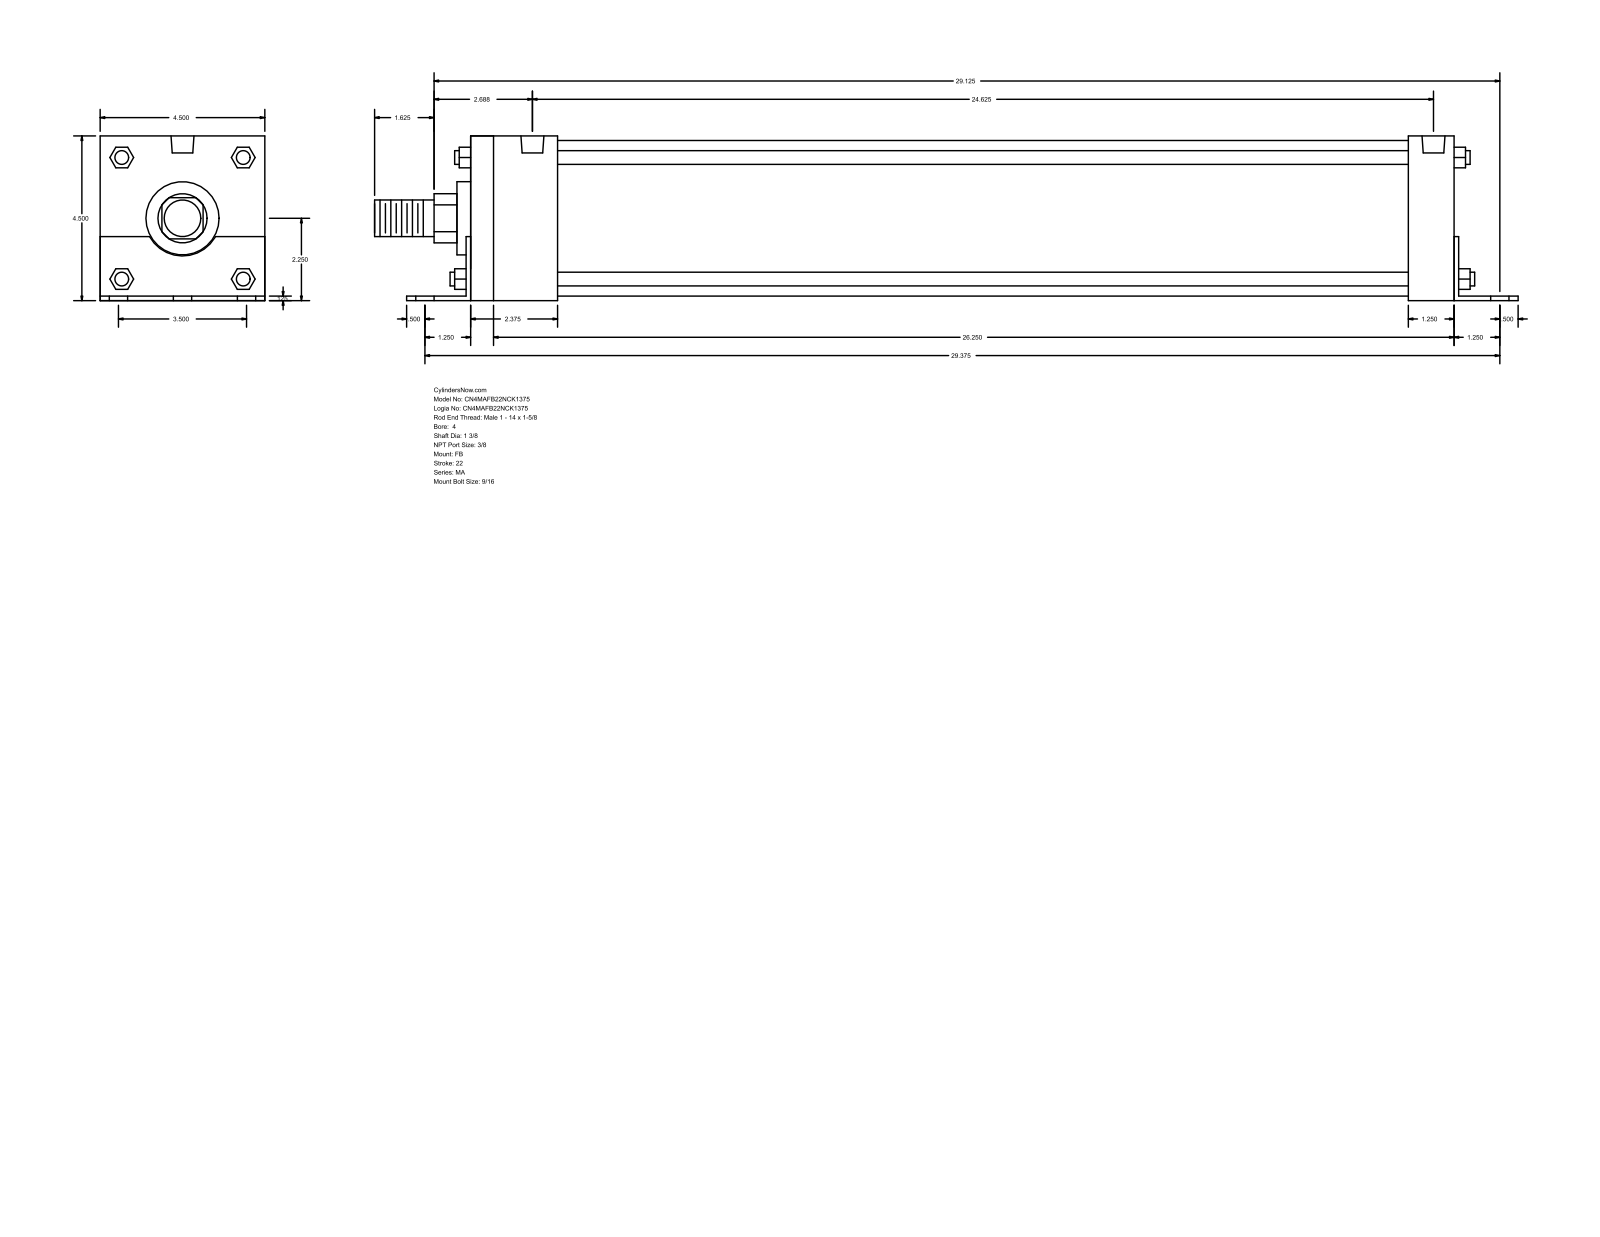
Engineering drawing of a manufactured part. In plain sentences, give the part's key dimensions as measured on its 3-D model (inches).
The part is named "MA_FB__0400_1.375". Its 3-D file was written by "GSSL Pune (CONFIG_CONTROL_DESIGN)". It is 0 solids with 140 faces: 105 planar, 35 cylindrical and 0 other. Overall it measures 31.25 by 4.502 by 4.5 inches. Round holes: 6 of diameter 0.563, 4 of diameter 0.437, 2 of diameter 0.627. Round bosses or shafts: 4 of diameter 0.375, 1 of diameter 4.25, 1 of diameter 2, 1 of diameter 1.375, 1 of diameter 1. Partial cylindrical surfaces (rounded edges, fillets, slot ends): 1 of radius 0.672, 1 of radius 1.03. The main face-to-face distances are 4.5, 0.125, 4.502, 0.123, 4.377, 26.875, 0.125, 27, 1.375, 27. The hole center spacings are 1.75, 29.427, 29.375, 2.519, 2.657, 3.419, 3.5, 3.582.
